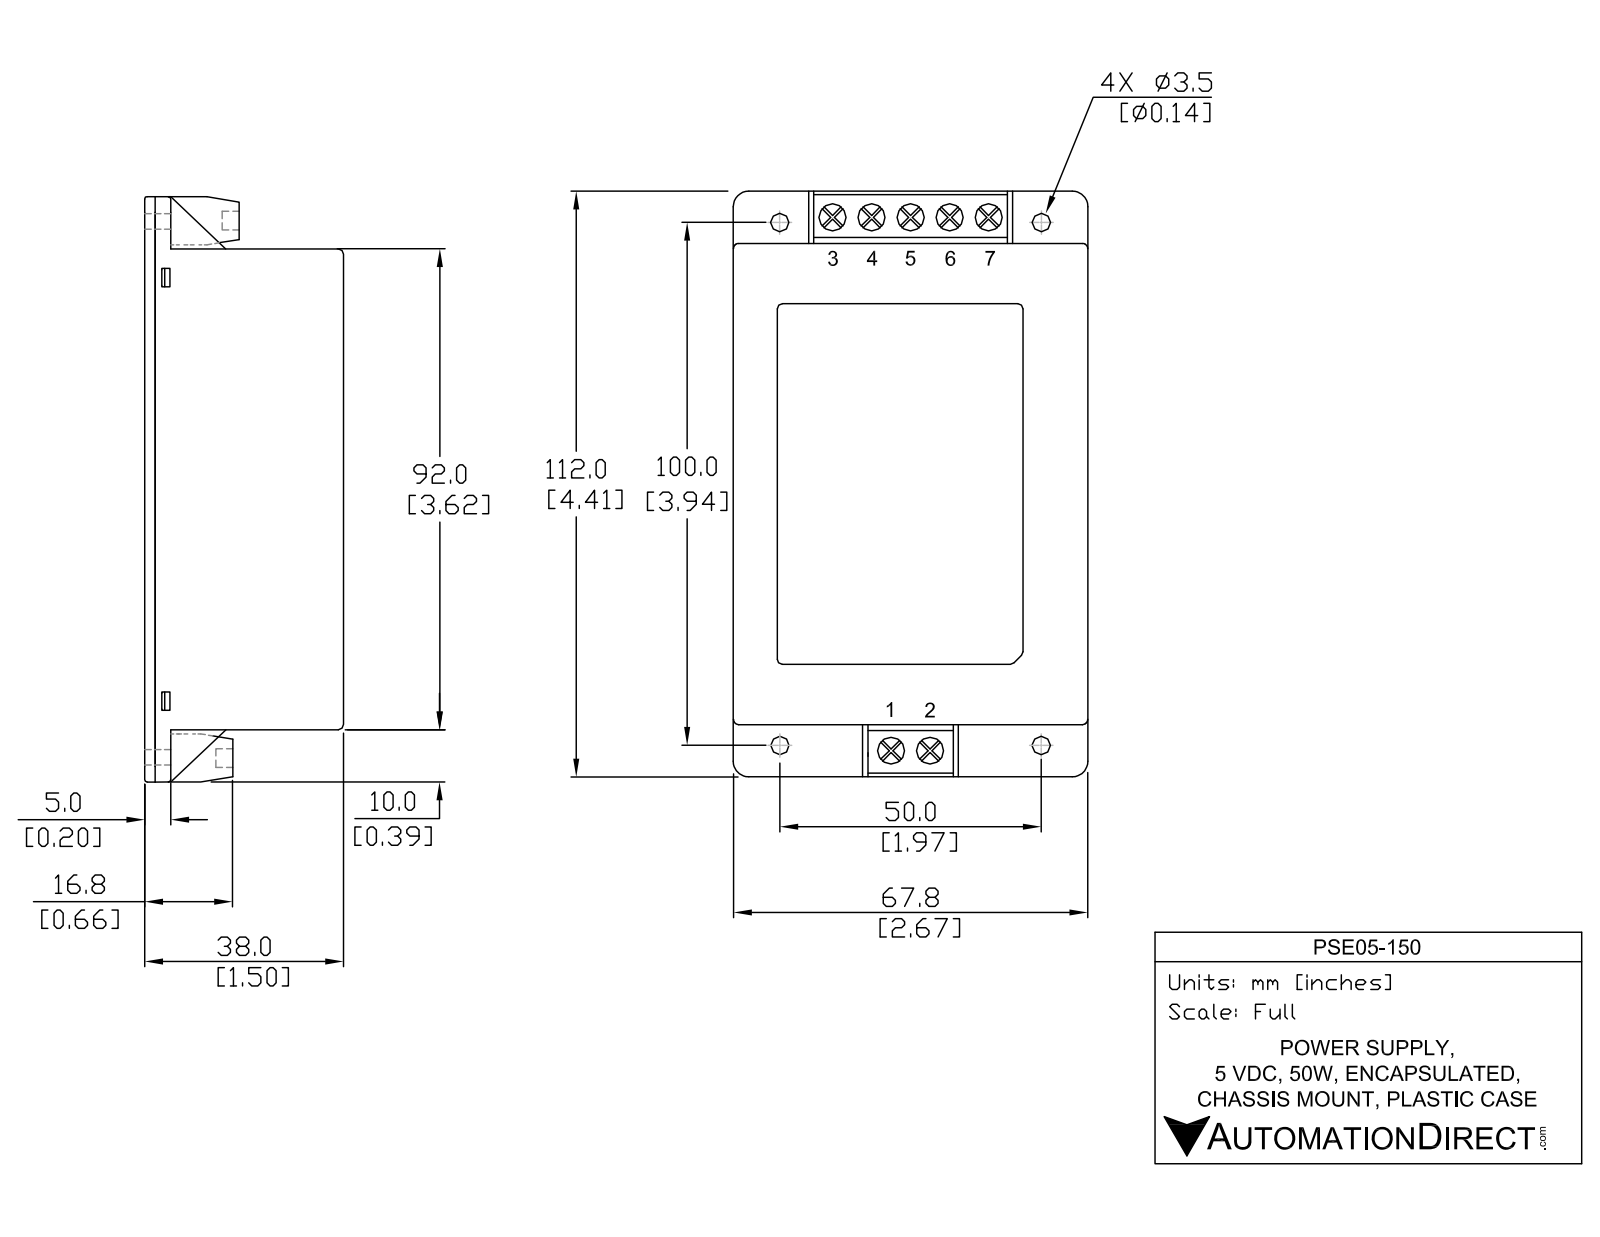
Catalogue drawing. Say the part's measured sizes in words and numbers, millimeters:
The part is named "PSE05-150". Its 3-D file was written by "SolidWorks 2011 (CONFIG_CONTROL_DESIGN)". It is 2 solids with 374 faces: 246 planar, 62 cylindrical and 66 other. Overall it measures 112 by 67.8 by 38.1 millimeters. Its volume is 248 800 cubic millimeters and its surface area 45 010 square millimeters. Round holes: 7 of diameter 5.1, 4 of diameter 3.6. Partial cylindrical surfaces (rounded edges, fillets, slot ends): 20 of radius 0.8, 4 of radius 3.2. The main face-to-face distances are 2, 2, 36.1, 67.8, 38, 36, 38.1, 36.1, 91.9, 0.4. The hole center spacings are 6.6, 13.2, 6.6, 21.7, 28.3, 50, 100.1, 102.
